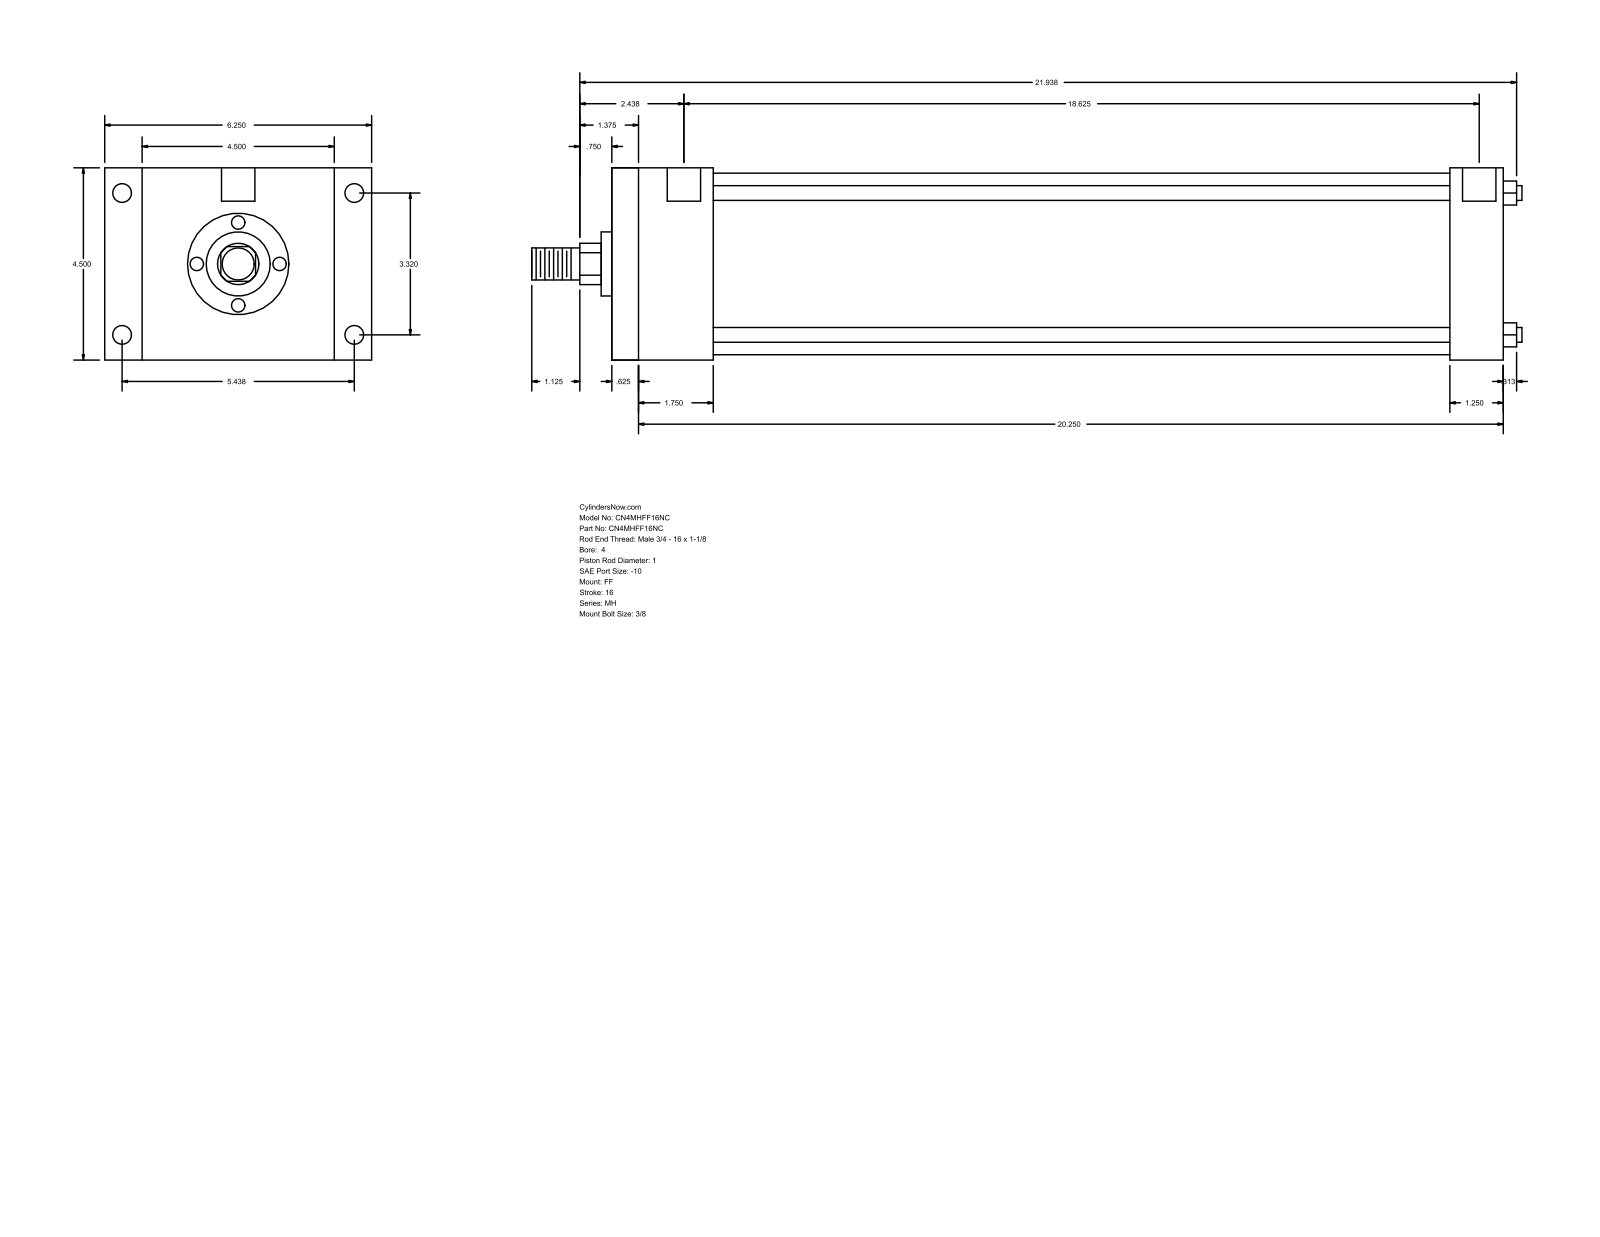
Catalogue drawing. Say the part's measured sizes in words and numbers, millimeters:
The part is named "MH_FF__0400_1". Its 3-D file was written by "GSSL Pune (CONFIG_CONTROL_DESIGN)". It is 0 solids with 92 faces: 64 planar, 28 cylindrical and 0 other. Overall it measures 588.96 by 158.75 by 114.3 millimeters. Round holes: 4 of diameter 8.73, 4 of diameter 11.13, 2 of diameter 19.84. Round bosses or shafts: 4 of diameter 8.76, 1 of diameter 107.95, 1 of diameter 38.1, 1 of diameter 25.4, 1 of diameter 19.05. Partial cylindrical surfaces (rounded edges, fillets, slot ends): 1 of radius 12.29. The main face-to-face distances are 114.3, 530.22, 15.87, 514.35, 60.33, 44.46, 469.89, 498.47, 482.6, 438.14. The hole center spacings are 84.32, 138.12, 161.82, 476.25, 1.58, 1.59, 473.08, 474.66.
